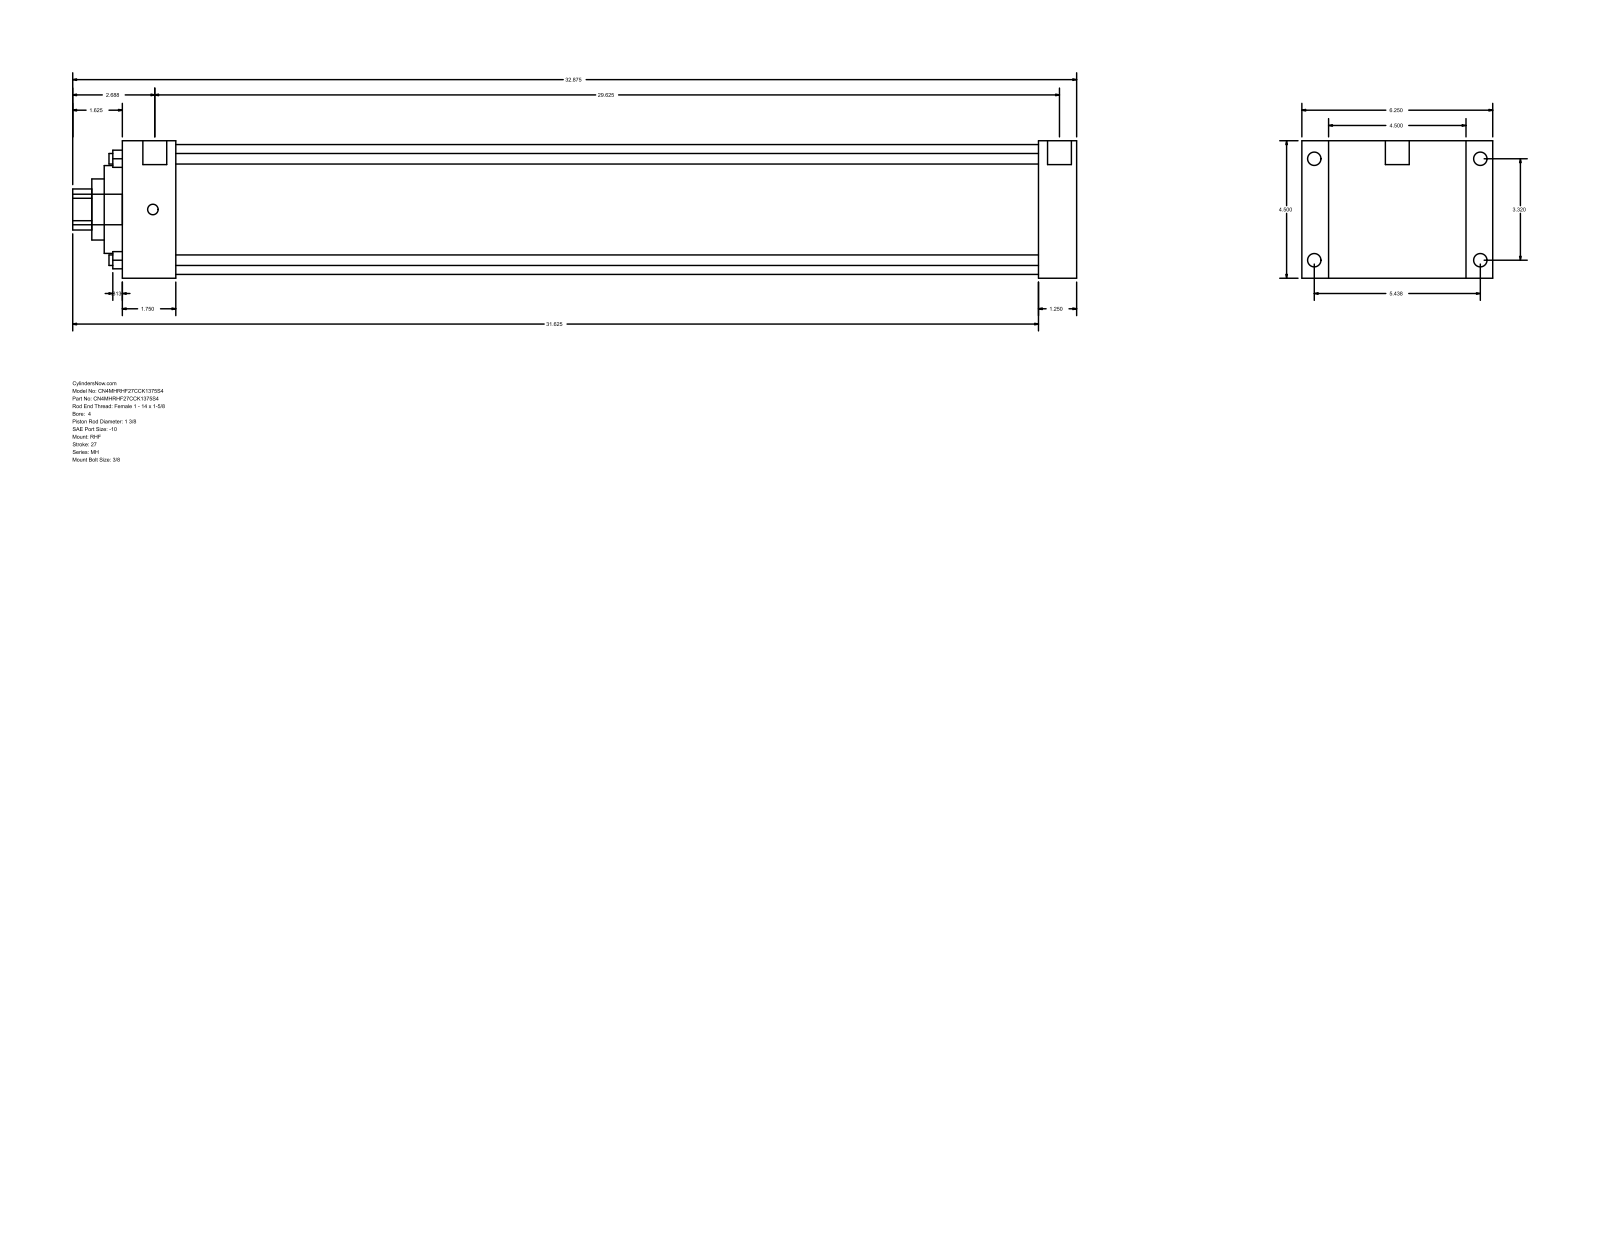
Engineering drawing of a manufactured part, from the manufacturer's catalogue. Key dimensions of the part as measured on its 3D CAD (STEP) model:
Part name (STEP PRODUCT): MH_RHF__0400_1.375
STEP written by: GSSL Pune (CONFIG_CONTROL_DESIGN)
Units: millimetres
Bodies: 0 solids, 90 faces (61 planar, 29 cylindrical, 0 other)
Overall size (bounding box): 835.02 × 158.75 × 114.3
Round holes (diameter × count): ⌀8.76 ×4, ⌀34.92 ×1, ⌀50.8 ×1, ⌀73.03 ×1, ⌀107.95 ×1
Round bosses / shafts (diameter × count): ⌀11.13 ×4, ⌀8.73 ×4, ⌀19.84 ×2, ⌀25.4 ×1
Partial cylindrical surfaces — rounded edges, fillets, slot ends (radius × count): R17.06 ×1
Main face-to-face distances: 114.3, 793.75, 762, 31.75, 22.23, 136.53, 44.45, 717.55, 749.3, 158.76
Hole centre spacings: 59.62, 84.32, 119.25
